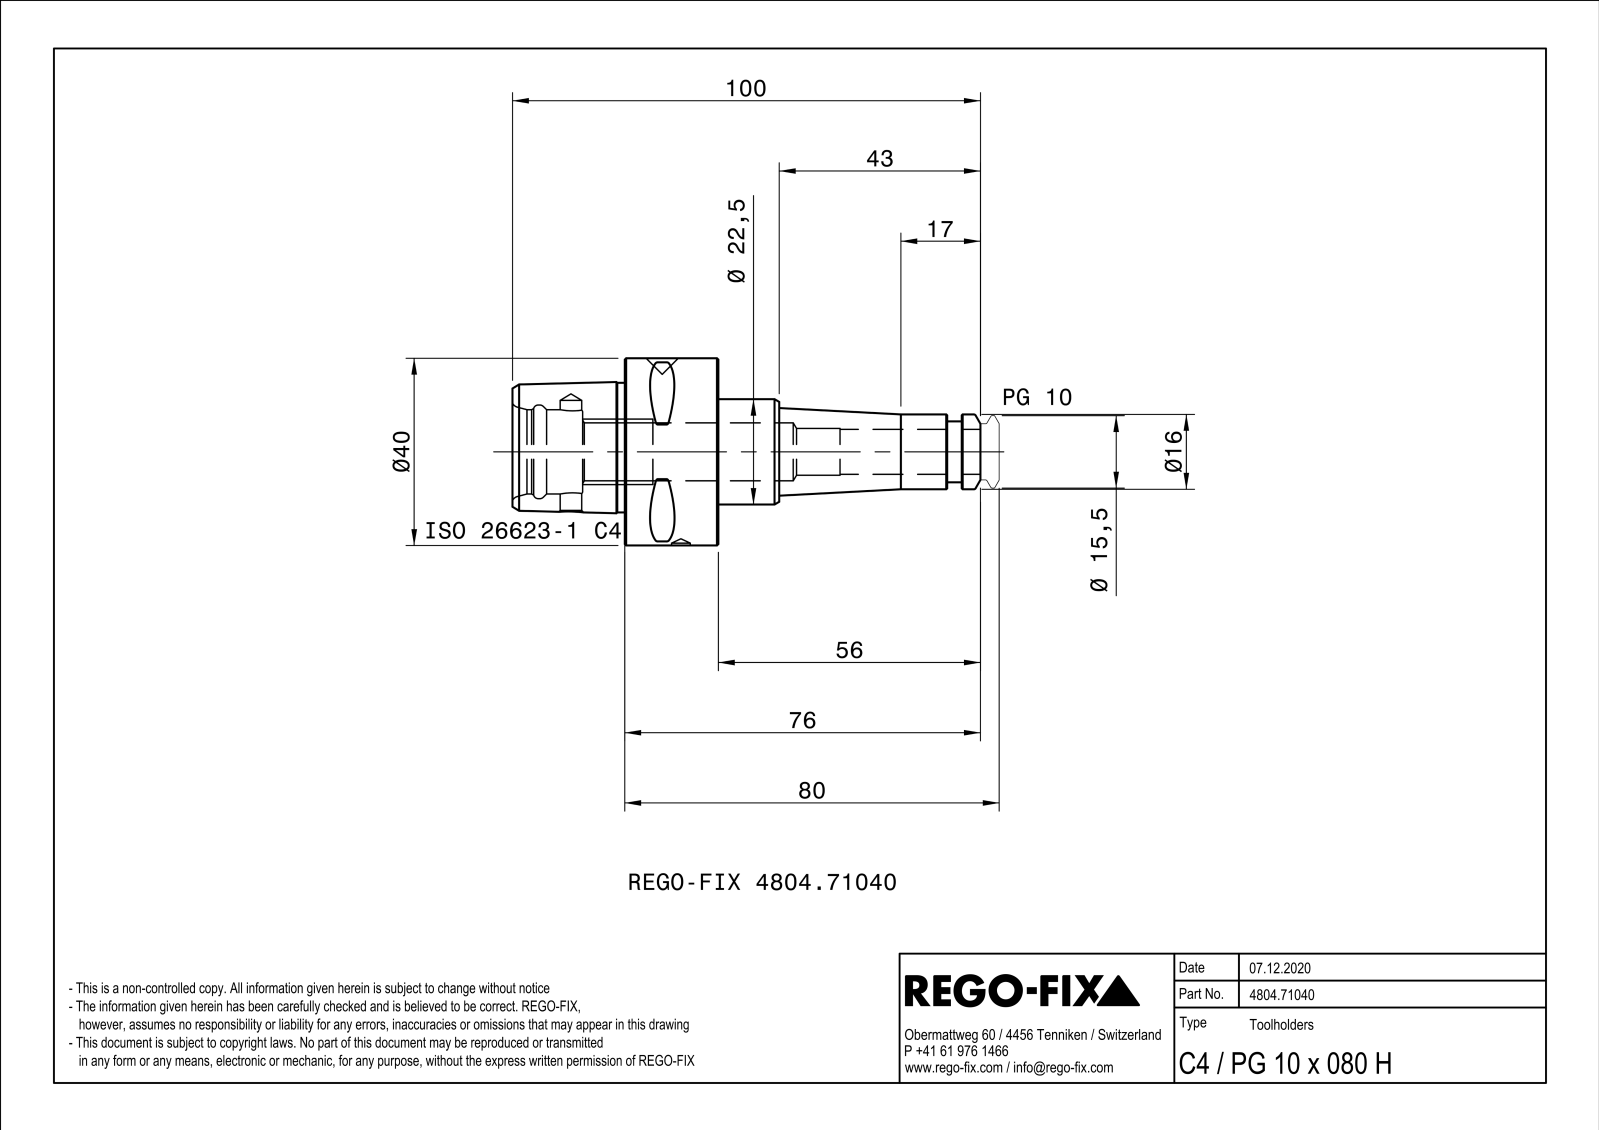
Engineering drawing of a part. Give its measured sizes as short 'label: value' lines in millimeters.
name: NOCUT
written by: SIEMENS PLM Software Solid Edge ST10 (AUTOMOTIVE_DESIGN)
unit: mm
bodies: 1 solid, 127 faces (24 planar, 25 cylindrical, 78 other)
size: 100 × 40 × 40
volume: 40 280 mm³; area: 14 007 mm²
holes: 1× ⌀4, 1× ⌀4.6, 1× ⌀10, 1× ⌀12.38, 1× ⌀18, 1× ⌀20
bosses: 1× ⌀40, 1× ⌀22.5, 1× ⌀16, 1× ⌀13
rounds: 8× R0.5, 1× R3
face distances: 20, 44, 24, 15.52, 29, 9, 15, 35.3, 3.1, 52
hole spacings: 23.5
